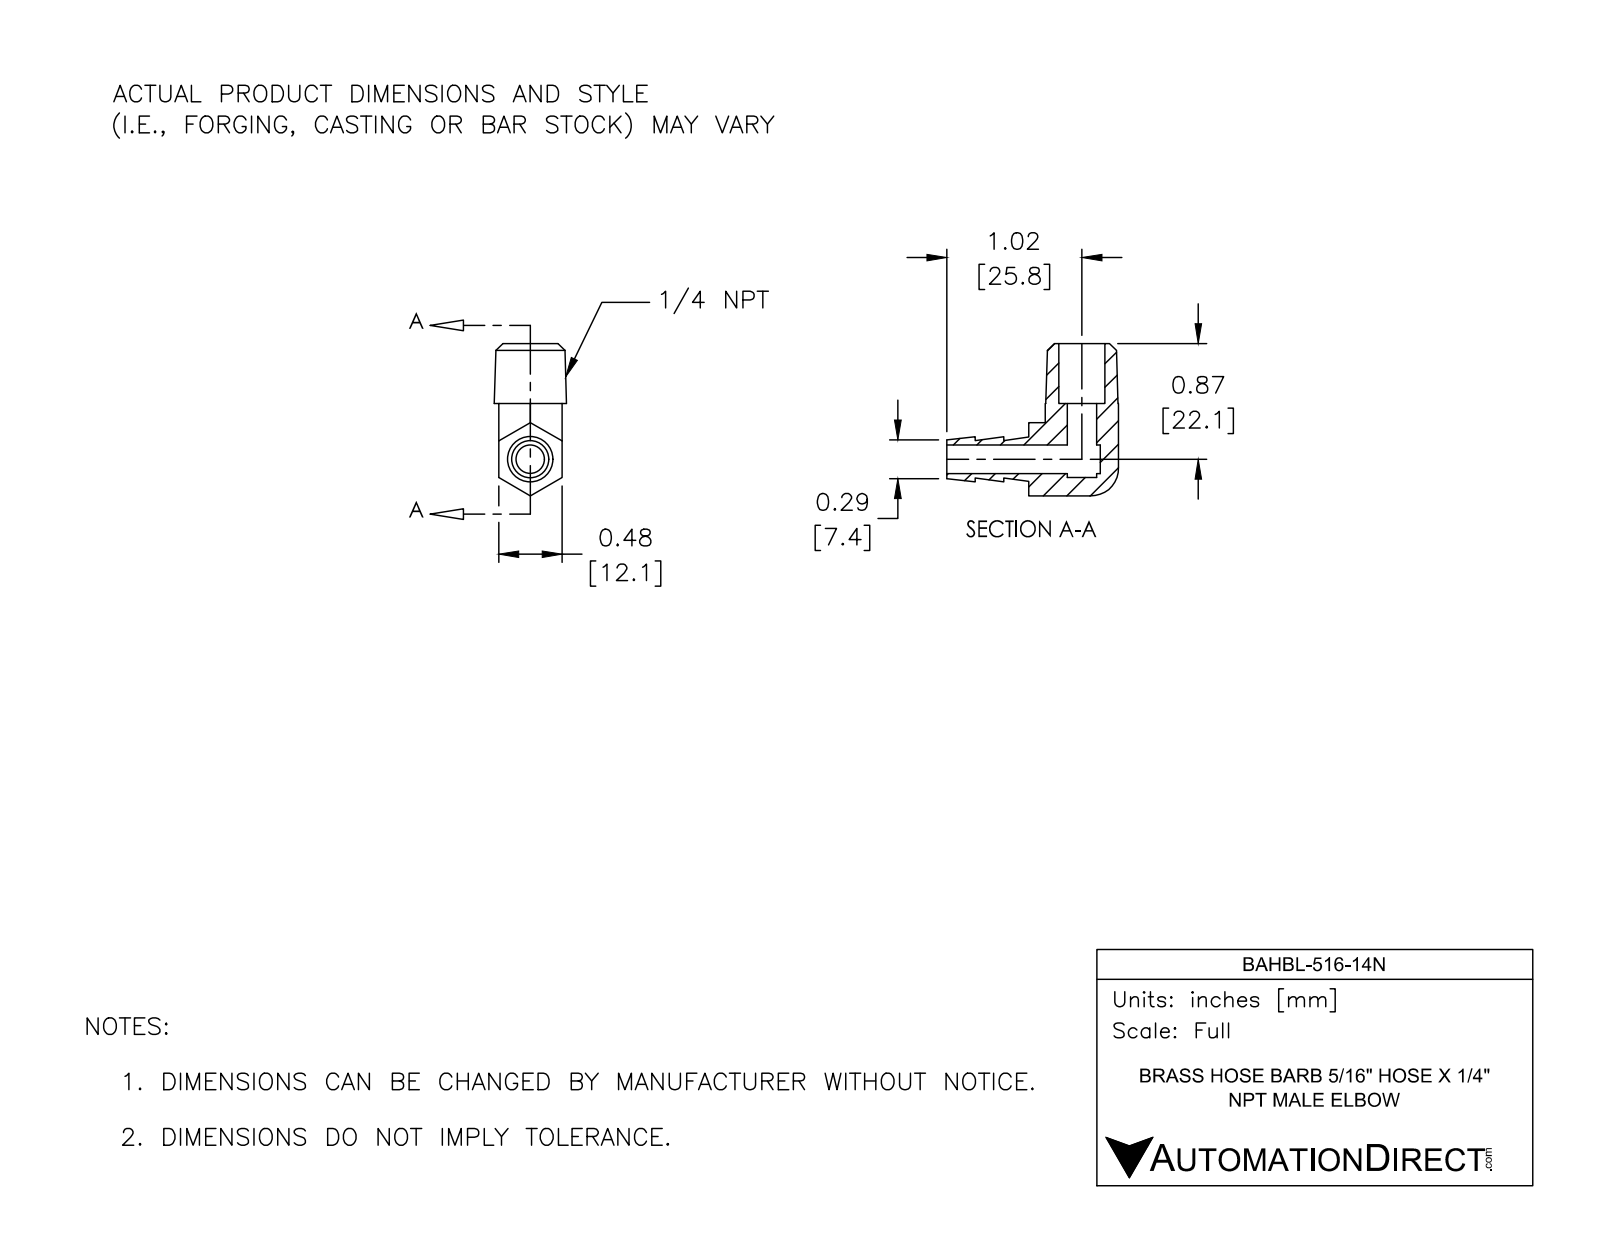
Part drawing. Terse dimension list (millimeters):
name: BAHBL-516-14N
written by: SolidWorks 2017 (AUTOMOTIVE_DESIGN)
unit: mm
bodies: 1 solid, 50 faces (30 planar, 10 cylindrical, 10 other)
size: 32.8 × 29.1 × 13.8
volume: 3 310 mm³; area: 2 932 mm²
holes: 1× ⌀5.5, 1× ⌀5.6, 1× ⌀8.8
rounds: 2× R6.4
face distances: 12.1, 11.4, 14.1, 25.6, 13.6, 18.4, 23.9, 4.8, 10.2, 5.4
